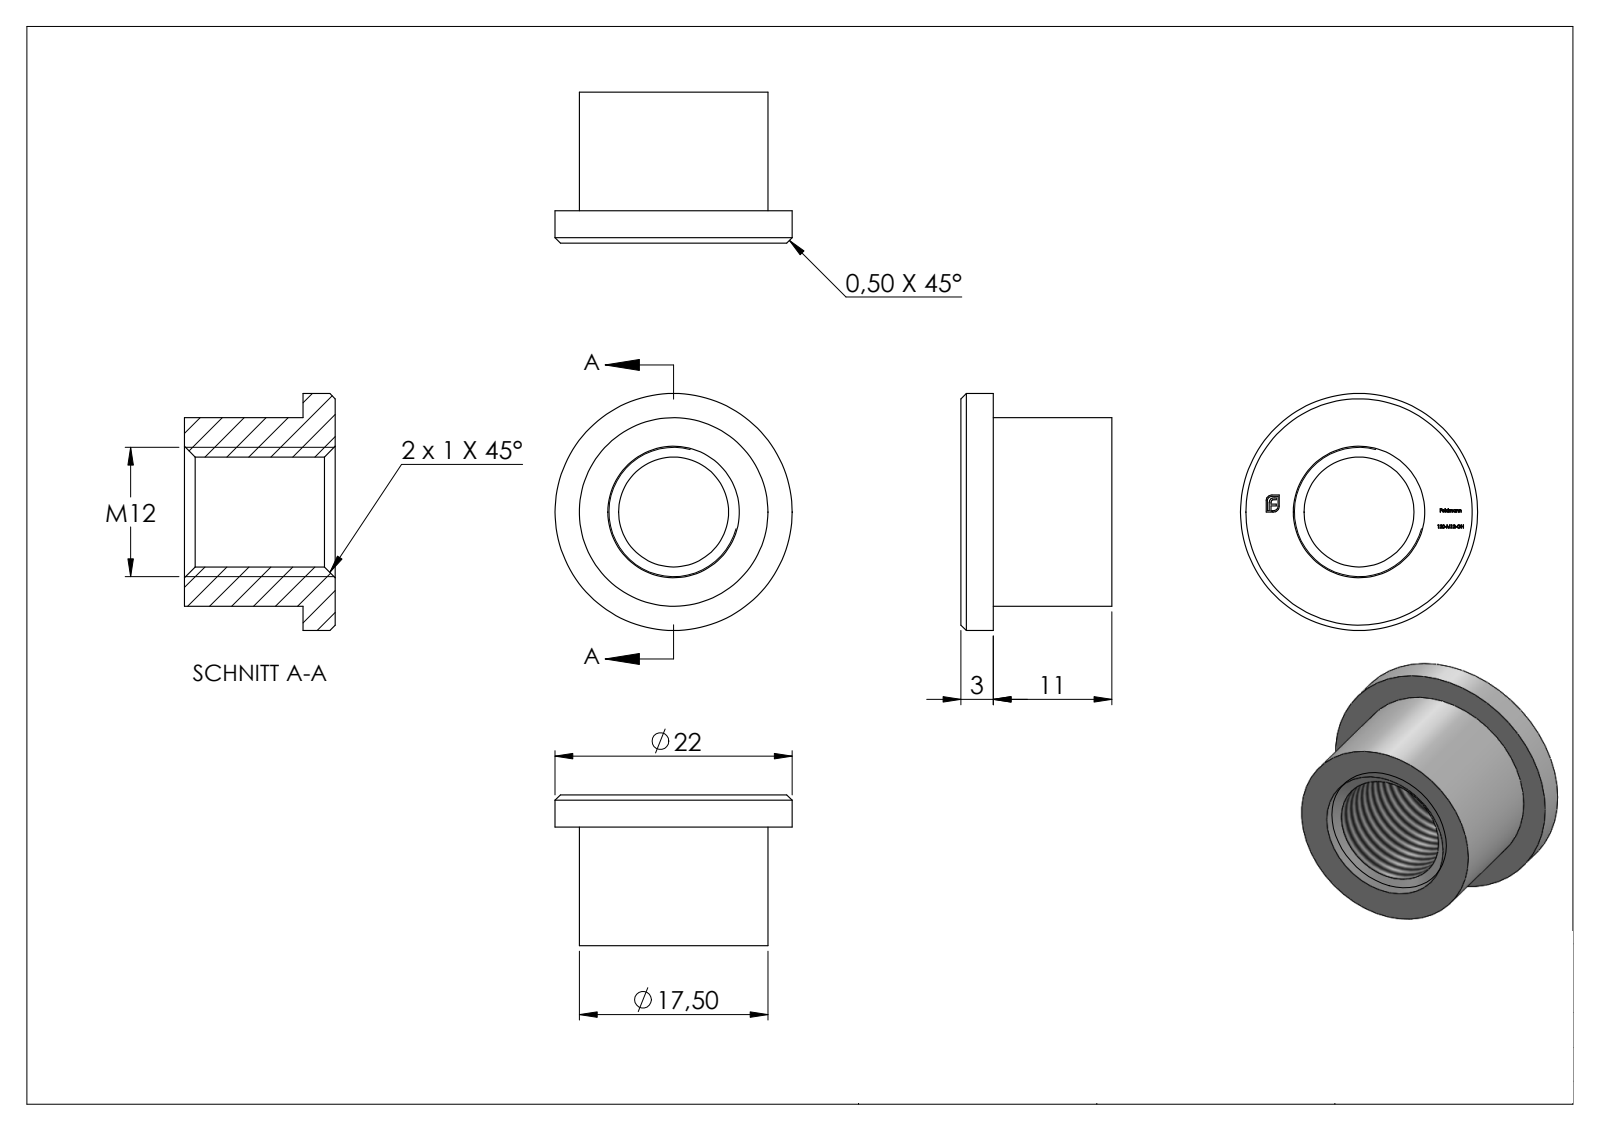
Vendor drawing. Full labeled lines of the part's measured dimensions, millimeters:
Part name (STEP PRODUCT): 120-M12-GH
STEP written by: SolidWorks 2018 (CONFIG_CONTROL_DESIGN)
Units: millimetres
Bodies: 1 solid, 273 faces (163 planar, 6 cylindrical, 104 other)
Overall size (bounding box): 22 × 22 × 14
Volume: 2 599 mm³ · Surface area: 1 806 mm²
Round holes (diameter × count): ⌀10.2 ×1
Round bosses / shafts (diameter × count): ⌀22 ×1, ⌀17.5 ×1
Main face-to-face distances: 3, 14, 11, 2.9, 13.9, 1.5, 1.47, 1.23, 0.47, 1.45
